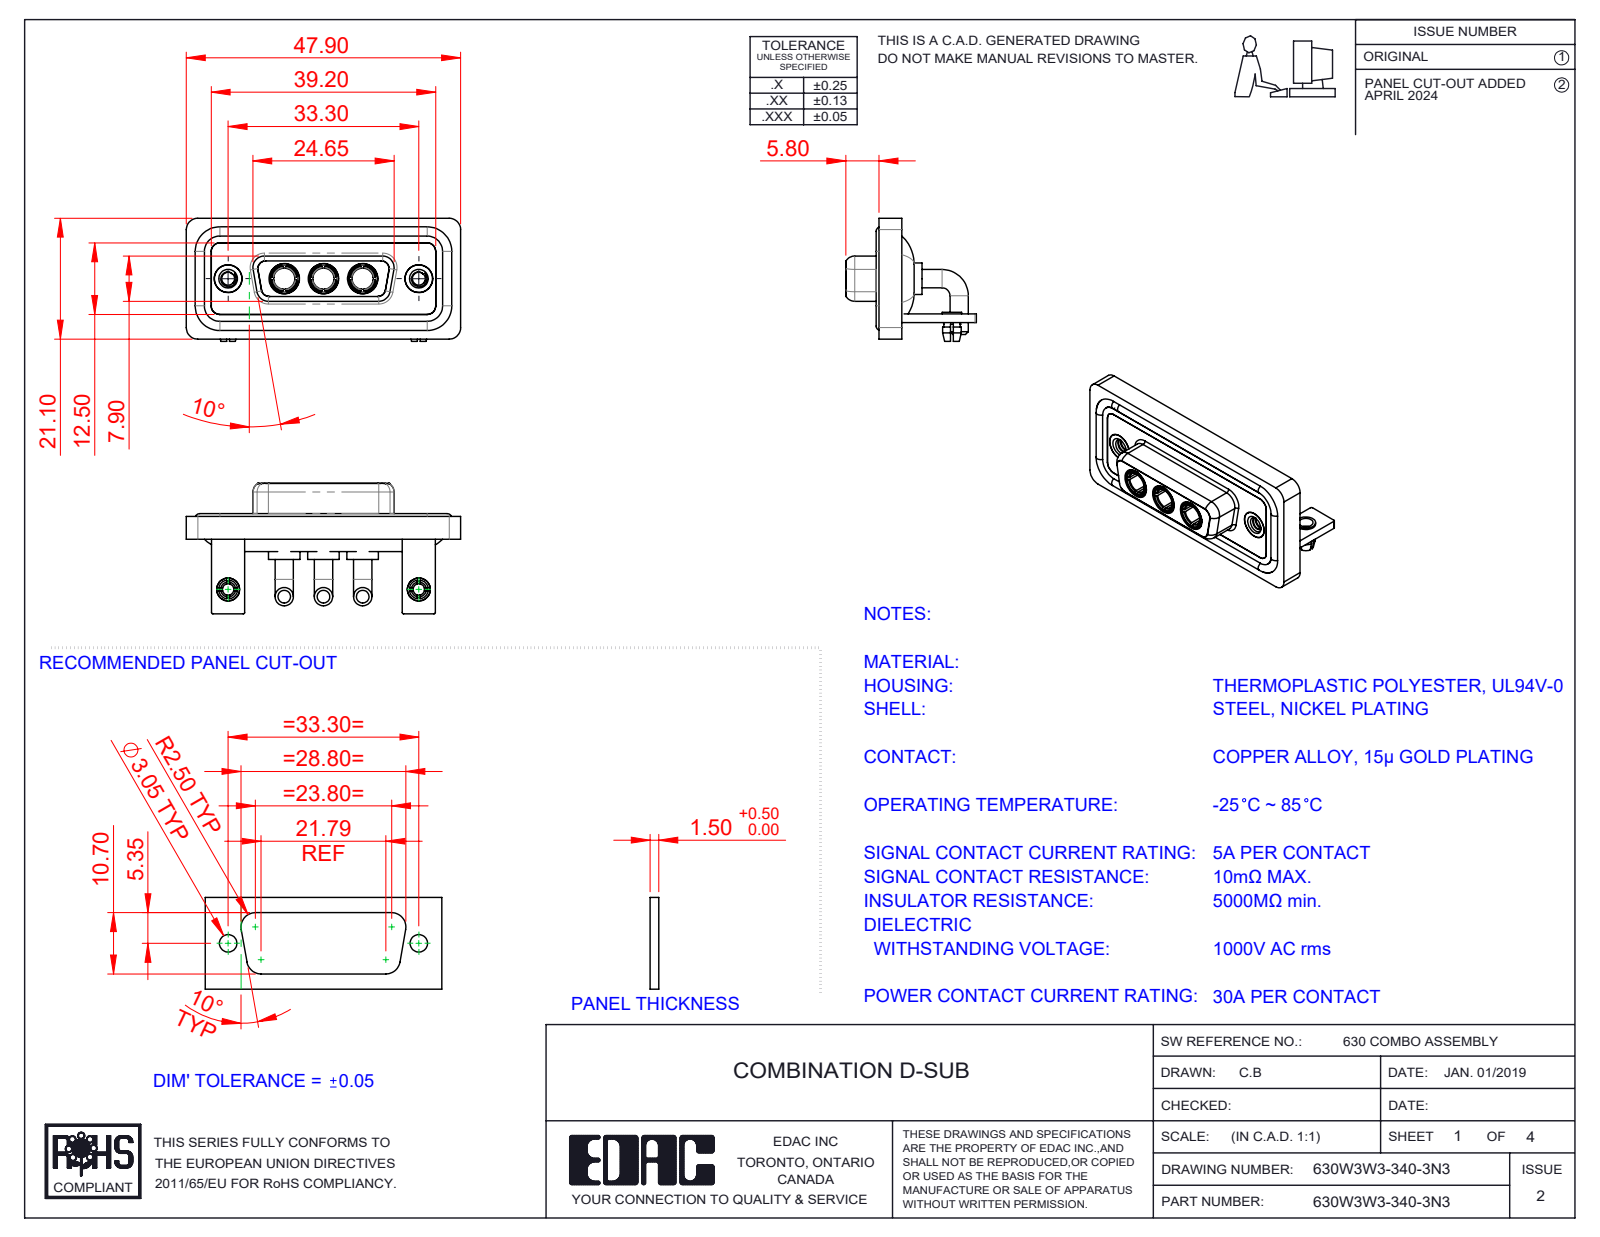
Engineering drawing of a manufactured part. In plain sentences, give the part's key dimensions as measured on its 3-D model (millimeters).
The part is named "630Combo Shell Front_15 Contacts; 630Combo Shell Rear_15 Contacts; Power Socket_30A RA; 630Combo Stabilizer Bracket_50 Contacts (+5 more)". Its 3-D file was written by "SolidWorks 2023 (CONFIG_CONTROL_DESIGN)". It is 17 solids with 760 faces: 260 planar, 319 cylindrical and 181 other. Overall it measures 47.9 by 22.8 by 21.5 millimeters. Its volume is 6 667 cubic millimeters and its surface area 10 973 square millimeters. Round holes: 5 of diameter 4.85, 3 of diameter 3.7, 3 of diameter 5.3, 2 of diameter 2, 2 of diameter 2.26, 2 of diameter 2.5, 2 of diameter 3.2, 2 of diameter 4, 2 of diameter 4.05, 2 of diameter 5. Round bosses or shafts: 6 of diameter 3.2, 4 of diameter 1.6, 3 of diameter 5.5, 3 of diameter 5.2, 3 of diameter 4.96, 3 of diameter 4.75, 3 of diameter 3.75, 2 of diameter 4.95. Partial cylindrical surfaces (rounded edges, fillets, slot ends): 21 of radius 2, 18 of radius 1.5, 16 of radius 0.25, 12 of radius 1.35, 8 of radius 1.6, 5 of radius 0.5, 4 of radius 0.6, 4 of radius 0.65. The main face-to-face distances are 0.4, 2.9, 1.5, 1.8, 3.7, 1.1, 4.1, 1.6, 2.5, 1.4. The hole center spacings are 6.85, 9.8, 16.65, 23.5, 33.3, 13.7.
